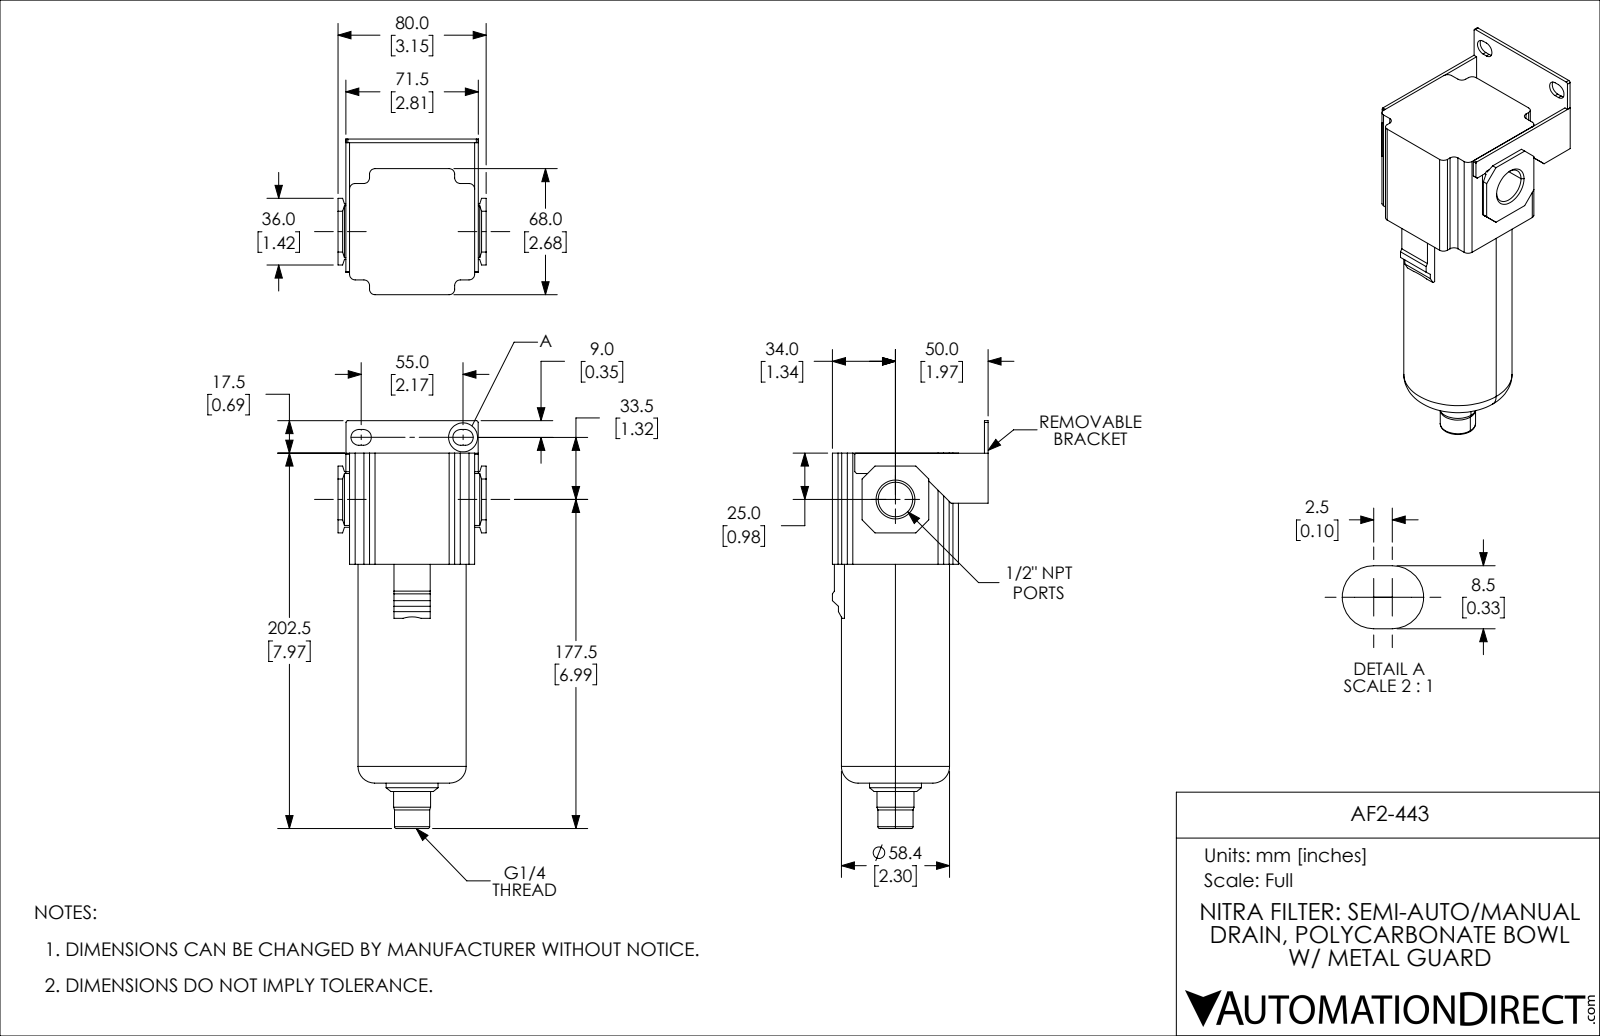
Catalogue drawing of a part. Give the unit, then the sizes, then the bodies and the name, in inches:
Units: inches
Overall size (bounding box): 8.661 × 3.307 × 3.15
Round holes (diameter × count): ⌀0.337 ×1, ⌀0.733 ×1
Round bosses / shafts (diameter × count): ⌀2.299 ×1, ⌀1.102 ×1, ⌀0.787 ×1, ⌀0.748 ×1
Partial cylindrical surfaces — rounded edges, fillets, slot ends (radius × count): R0.118 ×12, R0.167 ×4, R0.039 ×2
Main face-to-face distances: 0.079, 0.63, 2.362, 2.677, 3.307, 3.228, 2.736, 0.551, 2.657, 0.167
Volume: 35.99 in³ · Surface area: 94.57 in²
Bodies: 1 solid, 136 faces (90 planar, 32 cylindrical, 14 other)
Part name (STEP PRODUCT): AF2-443
STEP written by: SolidWorks 2019 (CONFIG_CONTROL_DESIGN)
